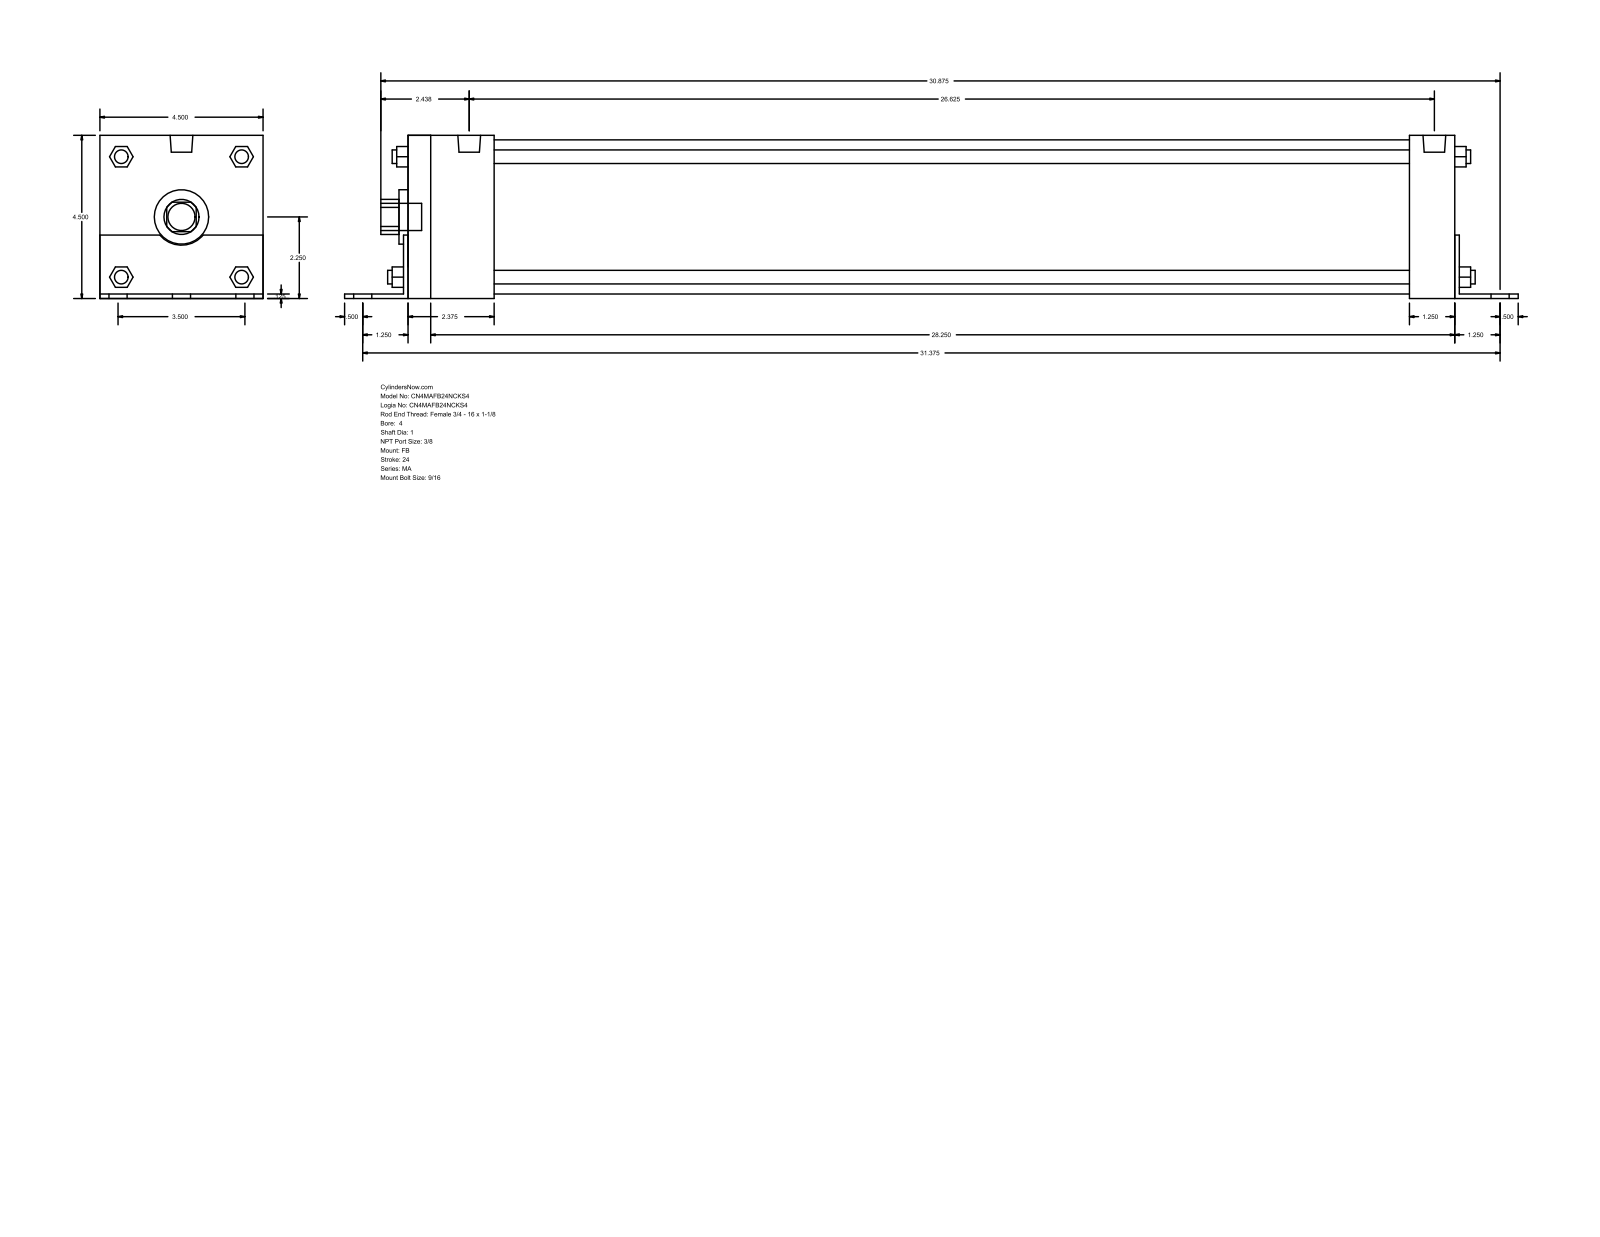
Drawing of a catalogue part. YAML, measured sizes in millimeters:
part_name: "MA_FB__0400_1"
step_written_by: "GSSL Pune (CONFIG_CONTROL_DESIGN)"
units: millimeters
bodies: {solids: 0, faces: 140, planar: 105, cylindrical: 35, other: 0}
overall_size: [822.33, 114.35, 114.3]
round_holes:
  - {diameter: 25.4, count: 1}
  - {diameter: 38.1, count: 1}
  - {diameter: 107.95, count: 1}
round_bosses_or_shafts:
  - {diameter: 14.29, count: 6}
  - {diameter: 11.11, count: 4}
  - {diameter: 9.53, count: 4}
  - {diameter: 15.93, count: 2}
  - {diameter: 19.05, count: 1}
partial_cylinders:
  - {radius: 12.29, count: 1}
  - {radius: 19.81, count: 1}
face_to_face_distances: [114.3, 3.17, 114.35, 736.6, 3.12, 111.18, 733.43, 739.77, 704.85, 701.68]
